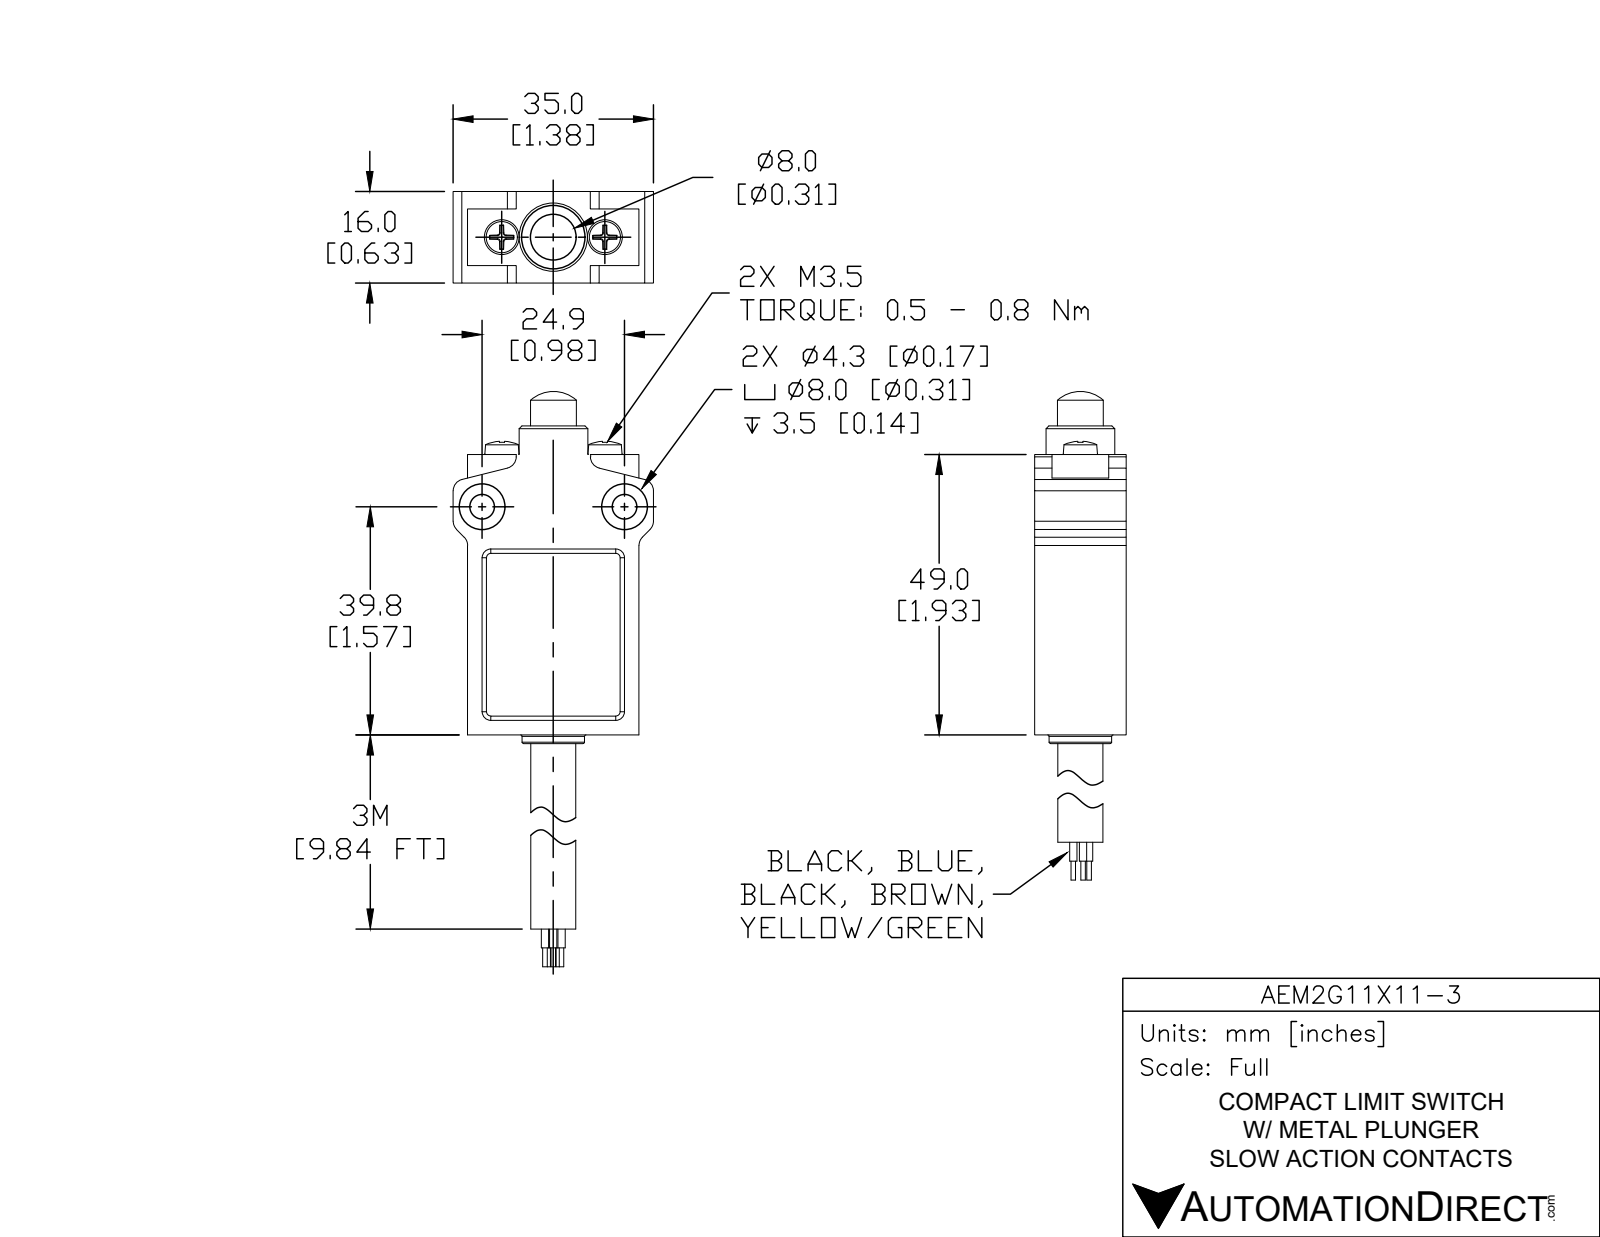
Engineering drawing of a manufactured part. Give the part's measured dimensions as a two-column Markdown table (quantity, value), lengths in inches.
| quantity | value |
| --- | --- |
| part name | AEM2G11X11-3_Default |
| STEP written by | SolidWorks 2021 (CONFIG_CONTROL_DESIGN) |
| units | inches |
| bodies | 1 solid, 99 faces (43 planar, 40 cylindrical, 16 other) |
| overall size | 2.96 × 1.38 × 0.63 |
| volume | 1.387 in³ |
| surface area | 10.9 in² |
| round holes (diameter × count) | 0.138 × 2, 0.177 × 2, 0.344 × 2 |
| round bosses / shafts (diameter × count) | 0.05 × 5, 0.031 × 5, 0.47 × 1, 0.43 × 1, 0.31 × 1 |
| partial cylindrical surfaces (radius × count) | 0.03 × 8, 0.08 × 8 |
| main face-to-face distances | 0.03, 0.6, 0.57, 0.63, 1.18, 1.93, 0.187, 0.443, 0.157, 0.413 |
| hole center spacings | 0.7, 0.98 |
